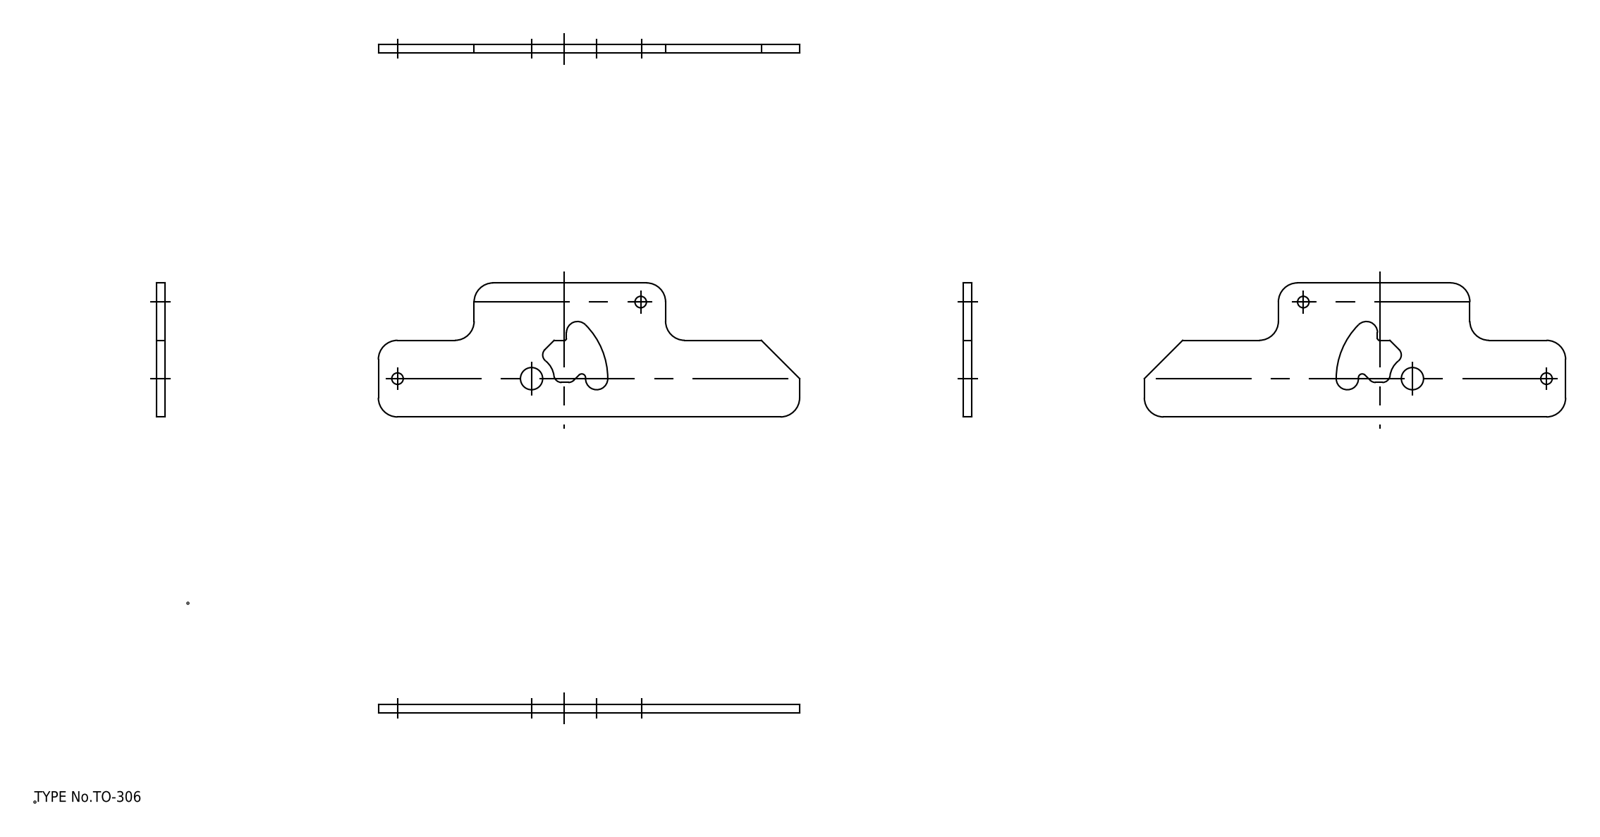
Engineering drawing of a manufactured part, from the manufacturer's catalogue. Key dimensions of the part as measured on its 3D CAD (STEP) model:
STEP written by: spGate 19.8.4 (****-****-****-****) (AUTOMOTIVE_DESIGN)
Units: millimetres
Bodies: 1 solid, 38 faces (16 planar, 22 cylindrical, 0 other)
Overall size (bounding box): 110 × 35 × 2.3
Volume: 6 103 mm³ · Surface area: 6 146 mm²
Round holes (diameter × count): ⌀3 ×2, ⌀5.8 ×1
Partial cylindrical surfaces — rounded edges, fillets, slot ends (radius × count): R5 ×7, R2 ×3, R2.9 ×2, R0.5 ×1, R1 ×1, R5.9 ×1, R19.9 ×1
Main face-to-face distances: 2.3, 35, 20, 15, 25, 75, 110, 50, 85, 11
Hole centre spacings: 34.82, 35, 66.58
